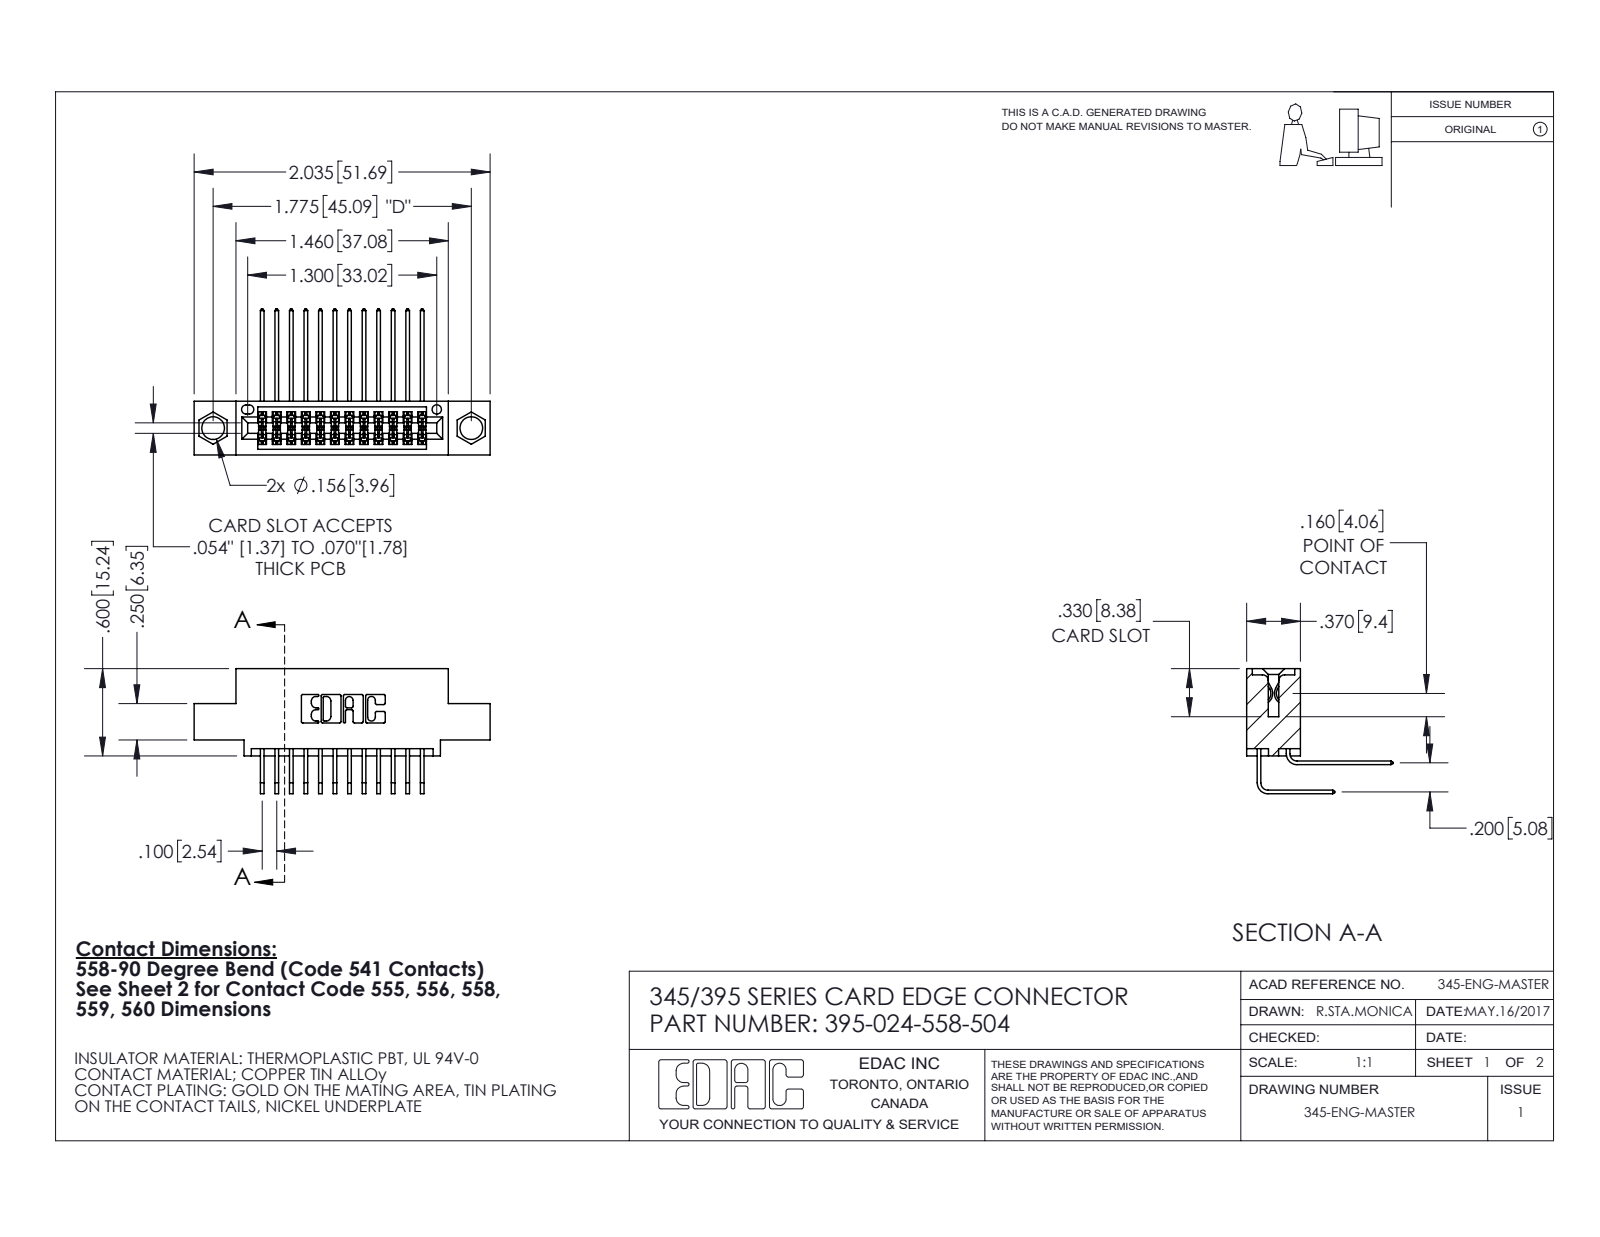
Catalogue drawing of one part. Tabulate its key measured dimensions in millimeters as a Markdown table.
| quantity | value |
| --- | --- |
| part name | 345 Part_0.110 Offset - 0.156 Dia-TI; 345-292-001_558 Tail - 2; 345-292-001_558 559 Tail - 1; 395-024-558-504 |
| STEP written by | SolidWorks 2020 (CONFIG_CONTROL_DESIGN) |
| units | millimeters |
| bodies | 25 solids, 1392 faces (938 planar, 454 cylindrical, 0 other) |
| overall size | 51.7 × 25.5 × 21.8 |
| volume | 4 700 mm³ |
| surface area | 6 961 mm² |
| round holes (diameter × count) | 4 × 2, 1.6 × 1 |
| partial cylindrical surfaces (radius × count) | 0.2 × 36, 0.3 × 22, 0.2 × 6, 0.8 × 6, 0.7 × 3, 0.4 × 2, 0.5 × 2, 0.6 × 2 |
| main face-to-face distances | 5.1, 1.8, 7.6, 9.4, 2.5, 6.9, 0.6, 5.7, 2.5, 4.1 |
| hole center spacings | 6.9, 39.2, 45.1 |
